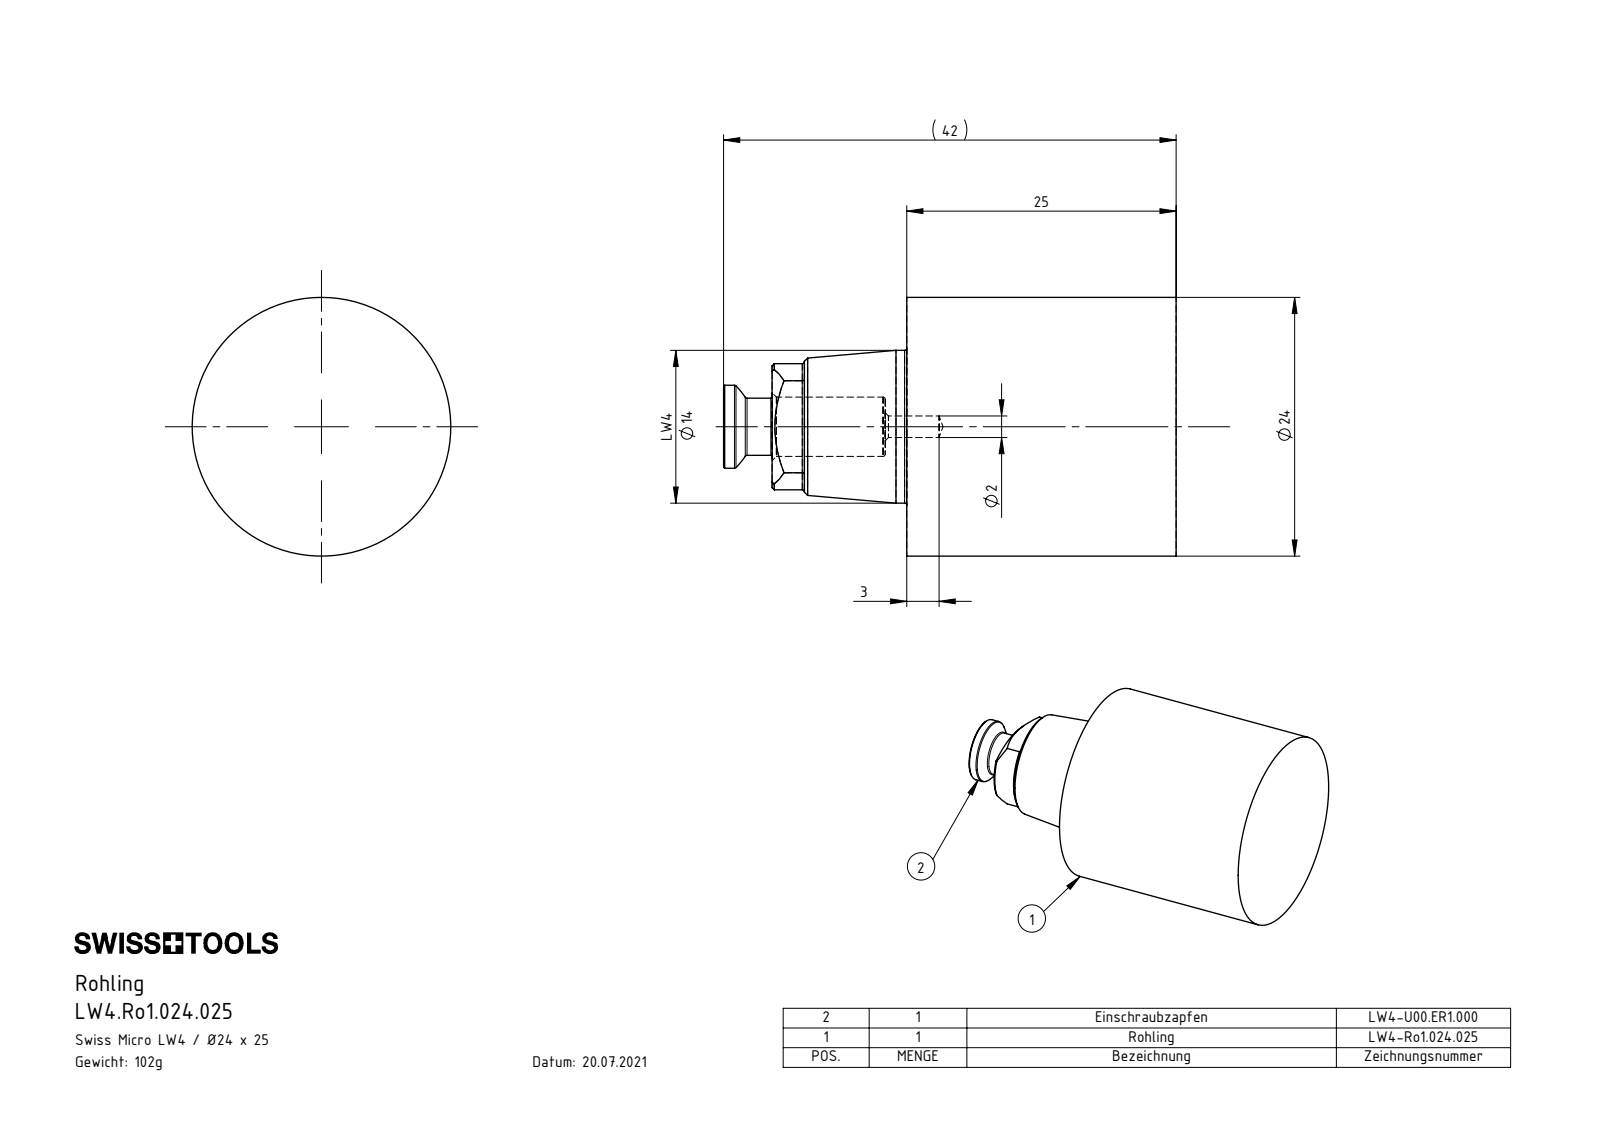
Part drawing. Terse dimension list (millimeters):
name: LW4.Ro1.024.025; LW4-U00.ER1.000_B; LW4-Ro1.024.025_A
written by: SolidWorks 2017 (AUTOMOTIVE_DESIGN)
unit: mm
bodies: 2 solids, 53 faces (15 planar, 13 cylindrical, 25 other)
size: 42 × 24 × 24
volume: 13 000 mm³; area: 3 911 mm²
holes: 1× ⌀2, 1× ⌀2.5, 1× ⌀5.5
bosses: 1× ⌀24, 1× ⌀14.17, 1× ⌀7.7, 1× ⌀6, 1× ⌀5.3, 1× ⌀5
rounds: 2× R0.2, 1× R5.85
face distances: 25, 7.5, 2, 12.5, 37.5, 4.5, 17, 42, 15, 10.5
